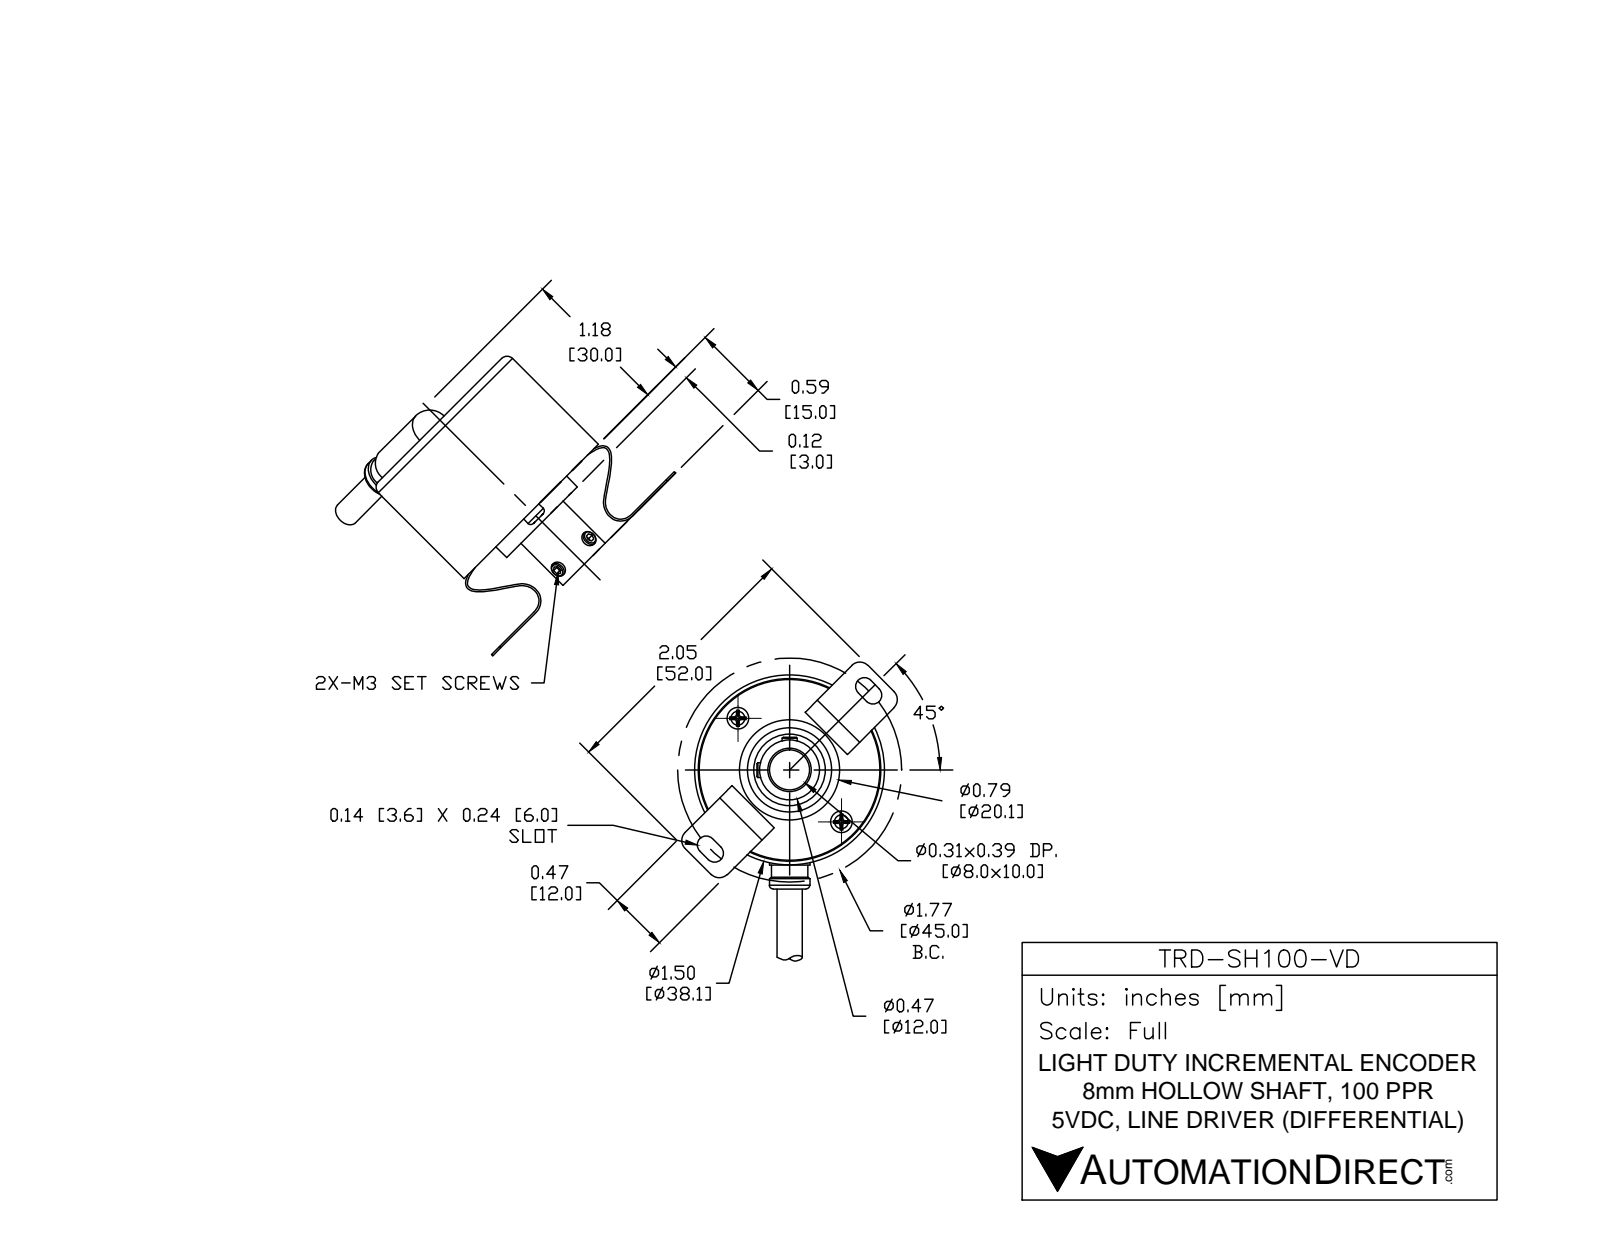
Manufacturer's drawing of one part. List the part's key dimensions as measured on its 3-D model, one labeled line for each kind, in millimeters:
Part name (STEP PRODUCT): TRD-SH
STEP written by: SolidWorks 2016 (AUTOMOTIVE_DESIGN)
Units: millimetres
Bodies: 1 solid, 278 faces (124 planar, 97 cylindrical, 57 other)
Overall size (bounding box): 100.39 × 45 × 42.77
Volume: 33 214 mm³ · Surface area: 9 709 mm²
Round holes (diameter × count): ⌀2.5 ×2, ⌀3.2 ×1, ⌀5.2 ×1, ⌀8 ×1, ⌀20.1 ×1
Round bosses / shafts (diameter × count): ⌀38 ×1, ⌀20 ×1, ⌀15 ×1, ⌀12 ×1, ⌀7.6 ×1, ⌀5 ×1, ⌀3 ×1
Partial cylindrical surfaces — rounded edges, fillets, slot ends (radius × count): R1 ×8, R3 ×5, R0.75 ×4, R1.8 ×4, R2.2 ×4, R2.5 ×4, R0.5 ×3, R2 ×3
Main face-to-face distances: 14.7, 26.3, 41, 40.7, 14.4, 15, 26, 12, 3, 29
Hole centre spacings: 14, 38
